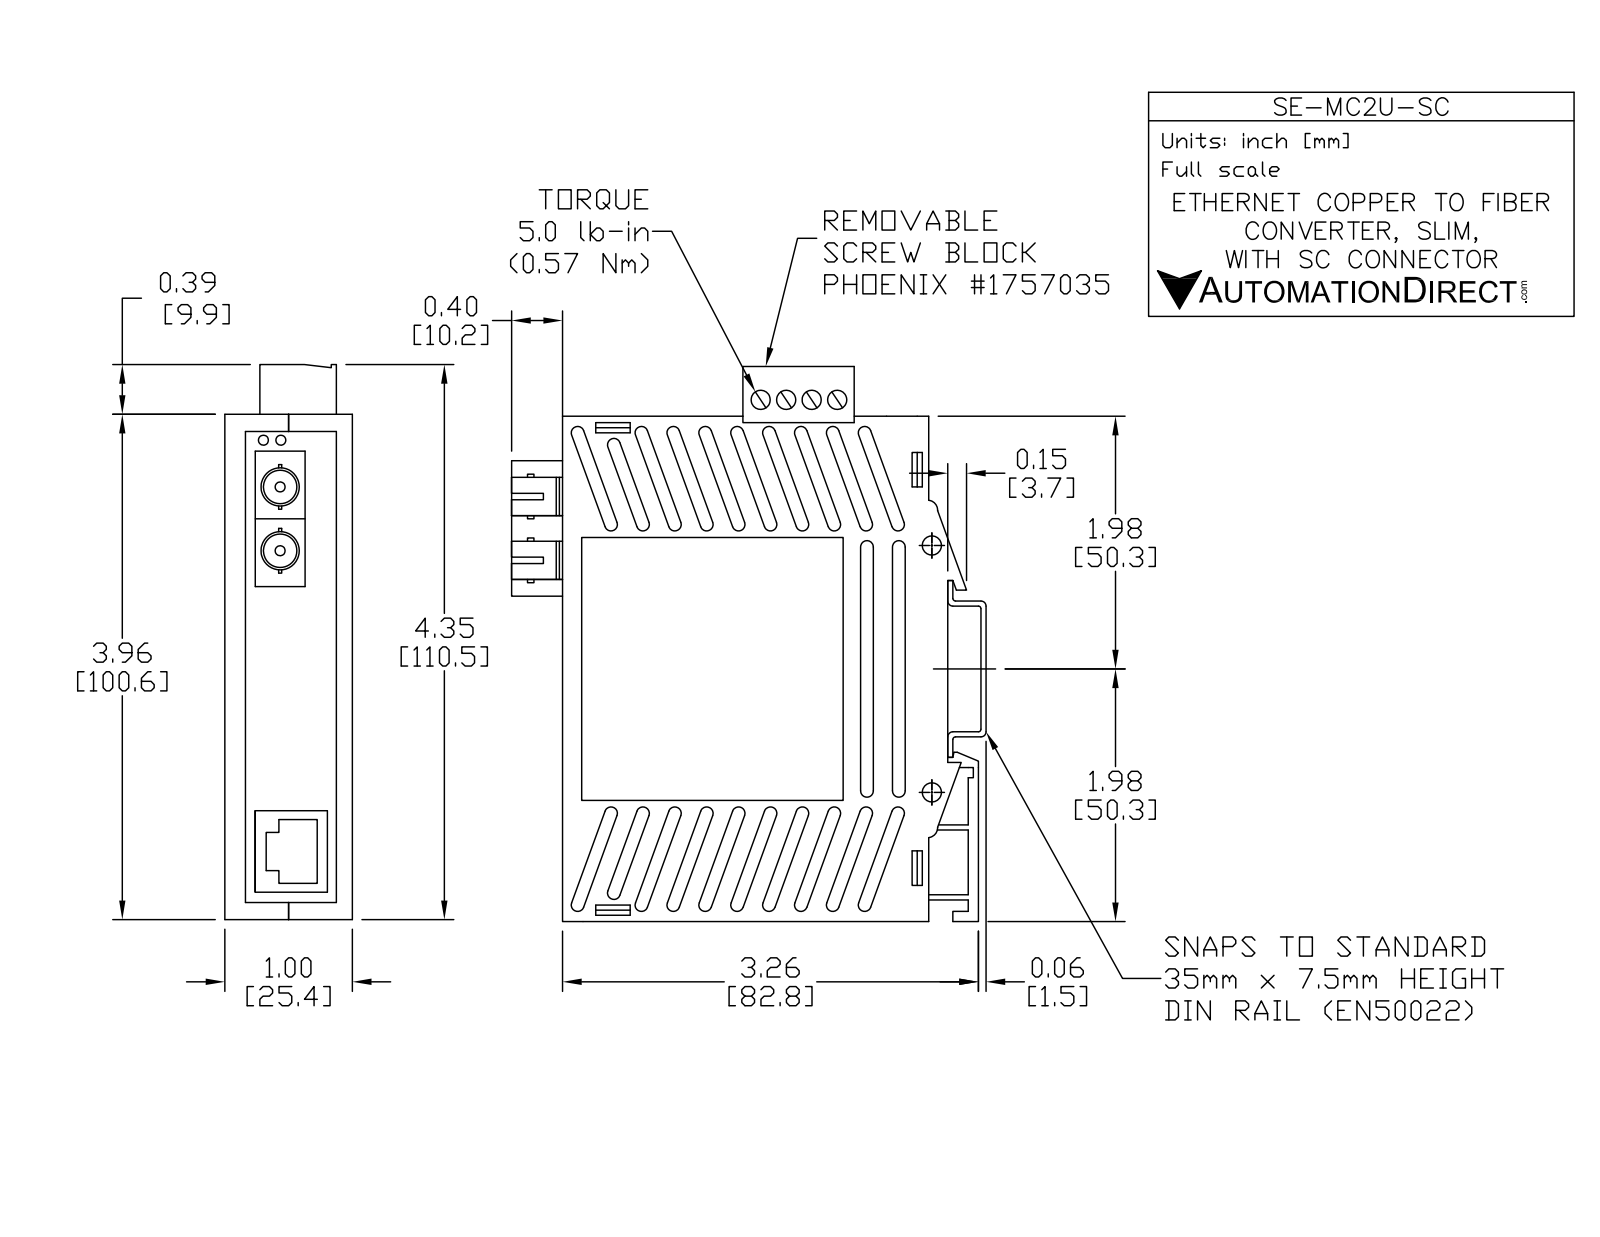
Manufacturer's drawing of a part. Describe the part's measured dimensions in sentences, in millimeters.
The part is named "SE-MC2U-SC". Its 3-D file was written by "SolidWorks 2011 (AUTOMOTIVE_DESIGN)". It is 24 solids with 1027 faces: 693 planar, 271 cylindrical and 63 other. Overall it measures 110.49 by 92.87 by 26.25 millimeters. Its volume is 35 006 cubic millimeters and its surface area 60 983 square millimeters. Round holes: 6 of diameter 3.81, 2 of diameter 3, 1 of diameter 2.05. Round bosses or shafts: 2 of diameter 4, 1 of diameter 5.81. Partial cylindrical surfaces (rounded edges, fillets, slot ends): 44 of radius 1.27, 44 of radius 2.27, 4 of radius 0.25, 2 of radius 1.25, 1 of radius 1.02, 1 of radius 1.05, 1 of radius 1.11, 1 of radius 2.02. The main face-to-face distances are 1, 25, 24.75, 1.25, 26, 23.75, 25.75, 26.25, 24, 25.25. The hole center spacings are 5.08, 10.16, 7.01, 13.1, 15.24, 34.57, 37.58, 41.01.
